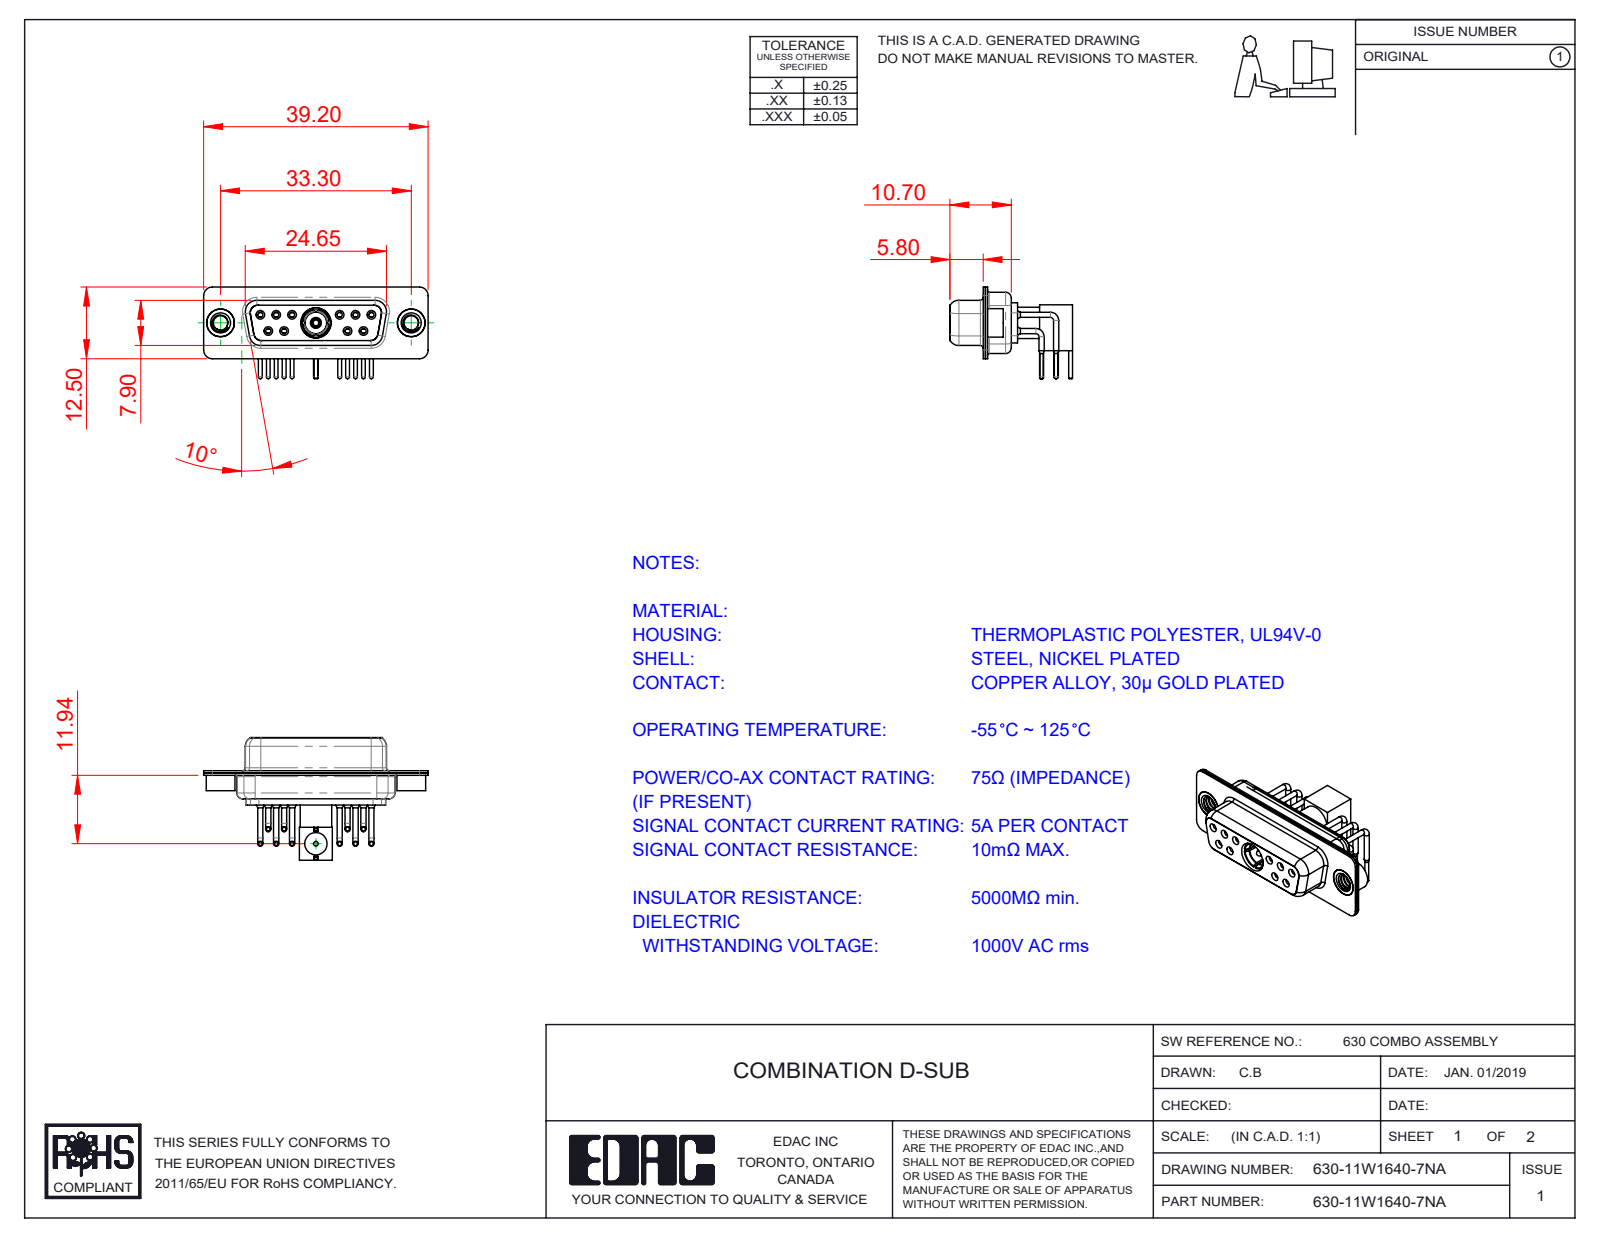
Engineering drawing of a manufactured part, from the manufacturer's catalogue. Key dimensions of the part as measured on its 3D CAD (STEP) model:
Part name (STEP PRODUCT): Locking Collar; Insulator RA Pin; Insulator Pin_Straight PC Tail; Co-Ax Plug Assy_RA (+8 more)
STEP written by: SolidWorks 2020 (CONFIG_CONTROL_DESIGN)
Units: millimetres
Bodies: 21 solids, 971 faces (284 planar, 430 cylindrical, 257 other)
Overall size (bounding box): 39.2 × 21.41 × 16
Volume: 2 805 mm³ · Surface area: 6 897 mm²
Round holes (diameter × count): ⌀1.1 ×11, ⌀1.5 ×11, ⌀0.9 ×10, ⌀2 ×10, ⌀1.7 ×6, ⌀1.6 ×4, ⌀4.85 ×3, ⌀2.5 ×2, ⌀4 ×2, ⌀4.05 ×2, ⌀0.8 ×1, ⌀2.83 ×1
Round bosses / shafts (diameter × count): ⌀0.9 ×10, ⌀0.65 ×10, ⌀1.6 ×6, ⌀5 ×3, ⌀4.95 ×2, ⌀4.8 ×2, ⌀5.5 ×1, ⌀5.2 ×1
Partial cylindrical surfaces — rounded edges, fillets, slot ends (radius × count): R1.5 ×16, R1.35 ×12, R2 ×12, R1.6 ×8, R0.25 ×4, R0.5 ×4, R0.6 ×4, R0.65 ×4
Main face-to-face distances: 0.4, 1.4, 0.45, 1.8, 8.45, 0.8, 8.9, 6.2, 7.05, 1.85
Hole centre spacings: 3.16, 2.77, 13.85, 11.08, 16.62, 5.03, 5.04, 5.54
